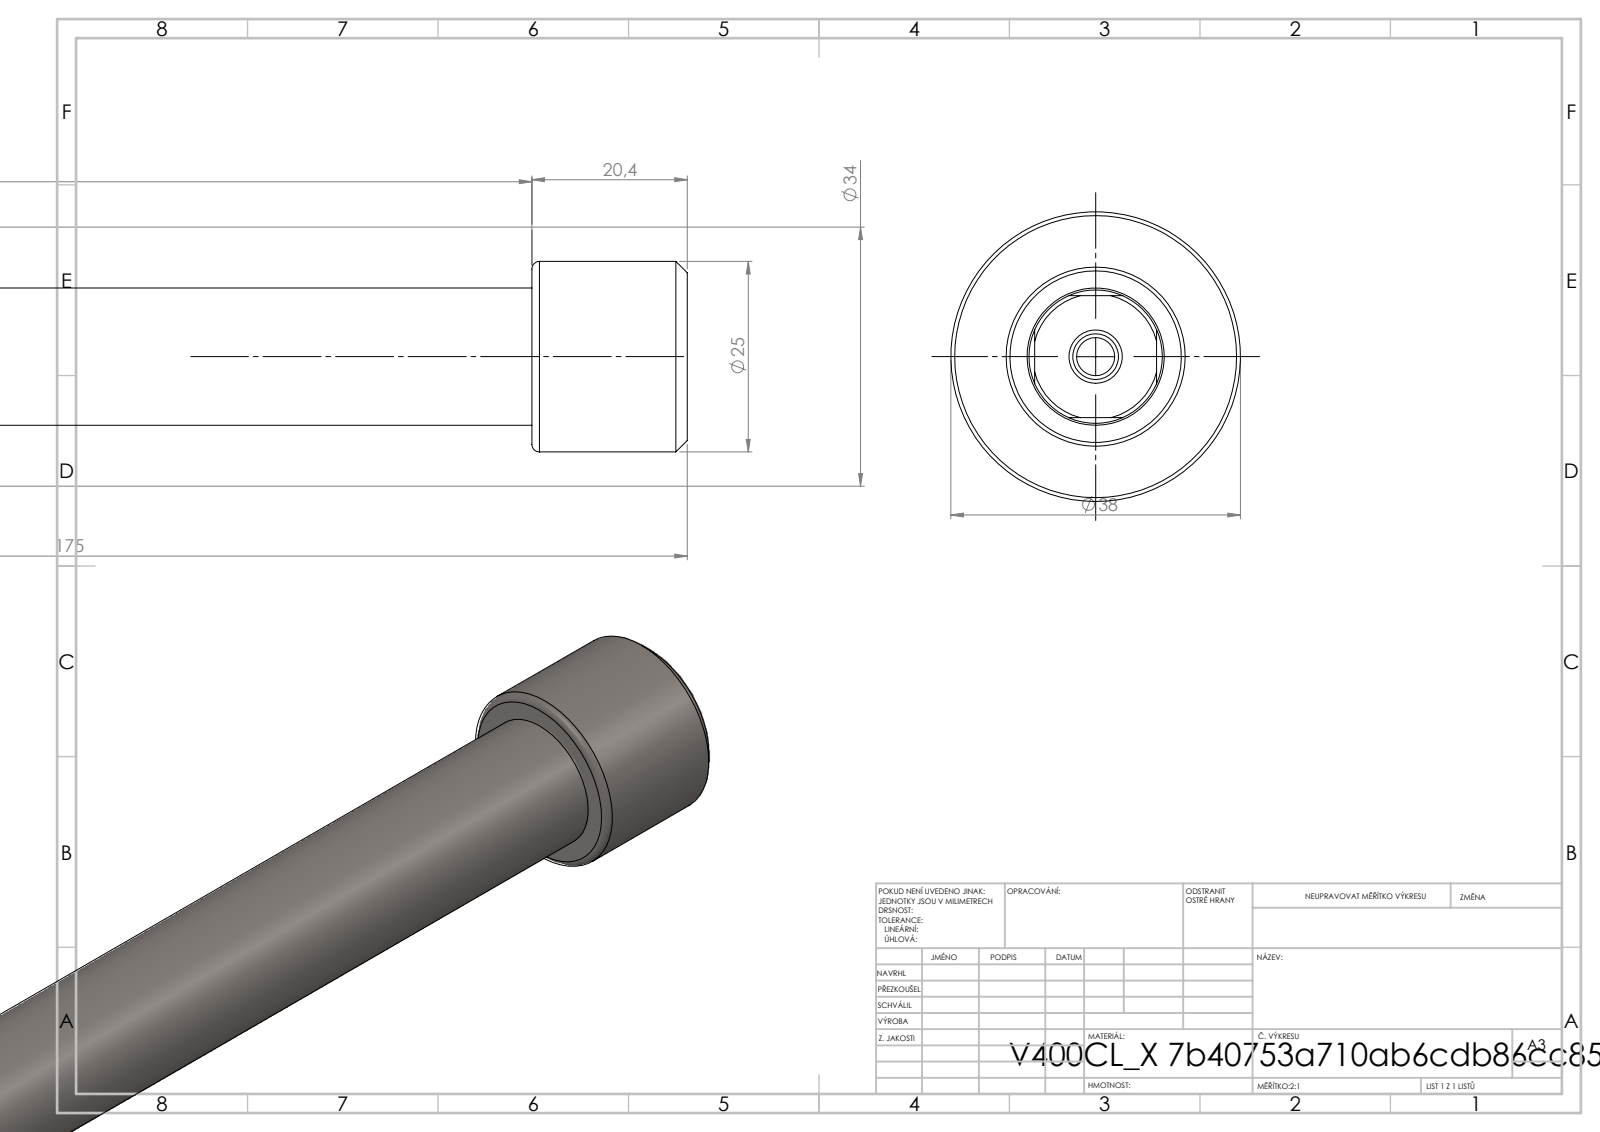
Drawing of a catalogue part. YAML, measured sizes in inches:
part_name: "V400CL_PC_X; V400CL_VC_X"
step_written_by: "SolidWorks 2019 (CONFIG_CONTROL_DESIGN)"
units: inches
bodies: {solids: 2, faces: 79, planar: 19, cylindrical: 30, other: 30}
overall_size: [6.89, 1.496, 1.496]
volume: 4.138
surface_area: 27.37
round_holes:
  - {diameter: 0.081, count: 1}
  - {diameter: 0.197, count: 1}
  - {diameter: 0.236, count: 1}
  - {diameter: 0.709, count: 1}
  - {diameter: 0.886, count: 1}
round_bosses_or_shafts:
  - {diameter: 1.496, count: 1}
  - {diameter: 1.339, count: 1}
  - {diameter: 1.299, count: 1}
  - {diameter: 0.984, count: 1}
partial_cylinders:
  - {radius: 0.344, count: 1}
face_to_face_distances: [5.608, 6.89, 1.281, 0.803, 4.805, 6.087, 6.593, 5.789, 0.984, 0.297]
